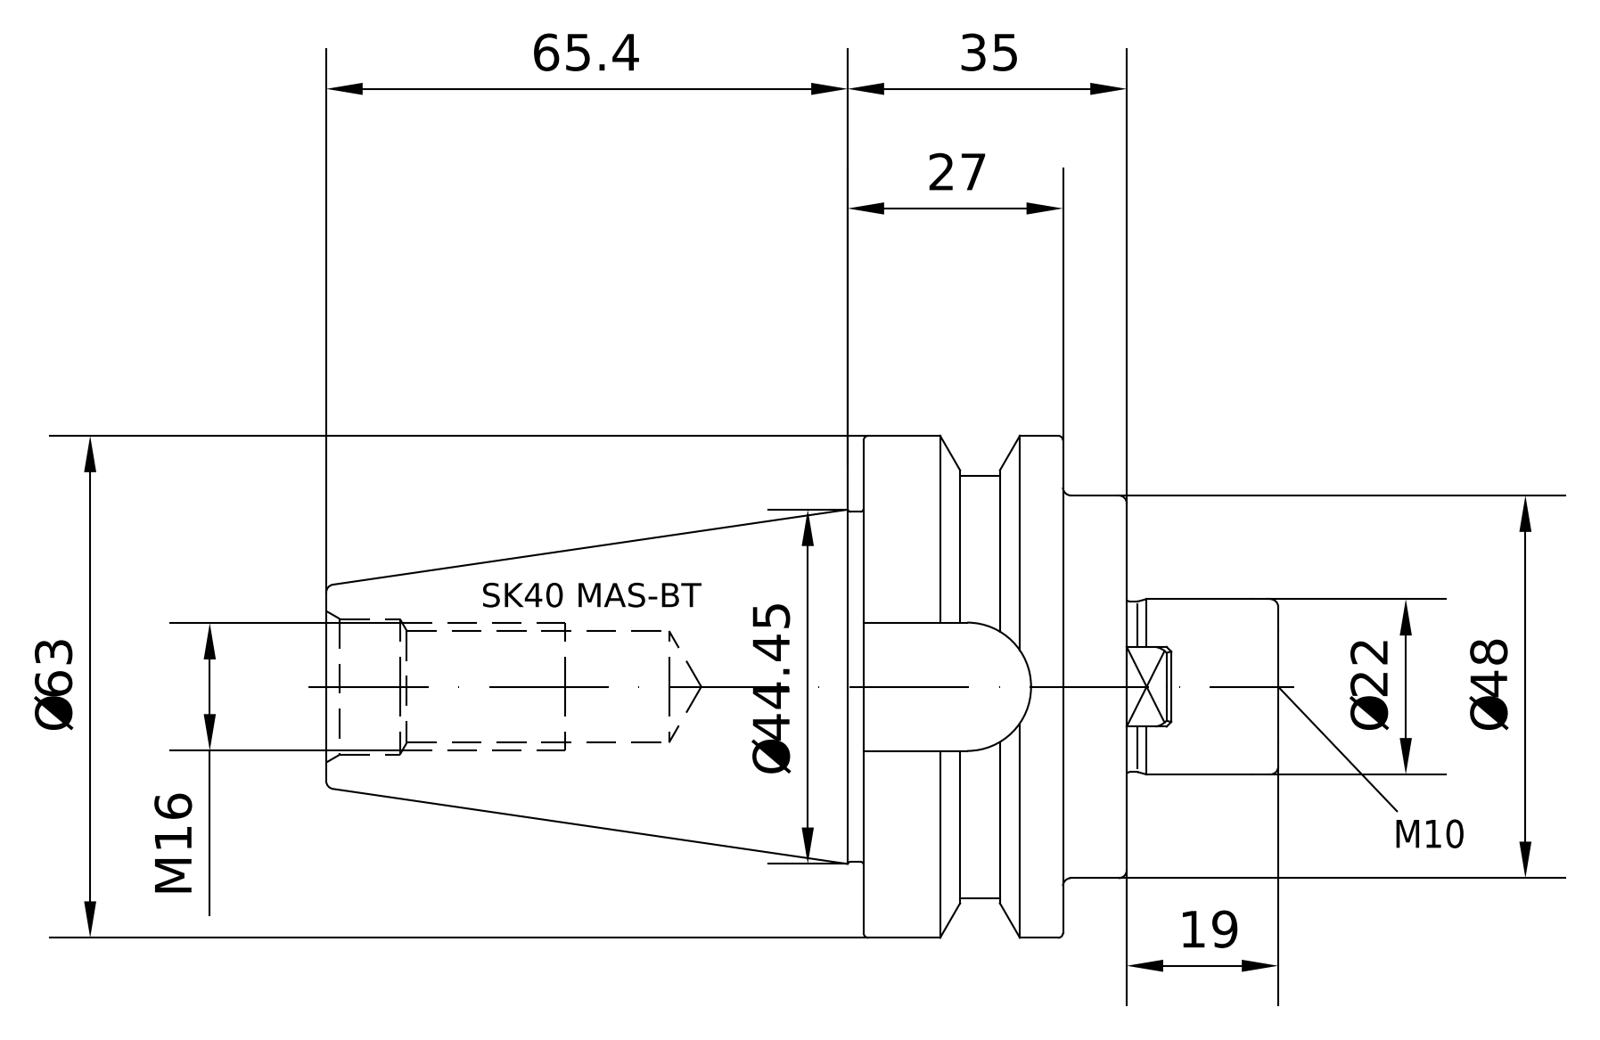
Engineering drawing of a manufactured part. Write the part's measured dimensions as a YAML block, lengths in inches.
part_name: "40-550-22"
step_written_by: "PRO/ENGINEER BY PARAMETRIC TECHNOLOGY CORPORATION, 2010430 (CONFIG_CONTROL_DESIGN)"
units: inches
bodies: {solids: 1, faces: 113, planar: 37, cylindrical: 26, other: 50}
overall_size: [4.701, 2.48, 2.48]
volume: 8.982
surface_area: 40.56
round_holes:
  - {diameter: 0.335, count: 1}
  - {diameter: 0.394, count: 1}
  - {diameter: 0.545, count: 1}
  - {diameter: 0.67, count: 1}
  - {diameter: 0.689, count: 1}
round_bosses_or_shafts:
  - {diameter: 2.48, count: 1}
  - {diameter: 2.077, count: 1}
  - {diameter: 1.89, count: 1}
  - {diameter: 1.722, count: 1}
  - {diameter: 0.866, count: 1}
  - {diameter: 0.63, count: 1}
partial_cylinders:
  - {radius: 0.319, count: 1}
face_to_face_distances: [1.299, 0.984, 0.315, 1.768, 2.047, 1.063, 0.748, 0.122, 0.516, 0.394]
